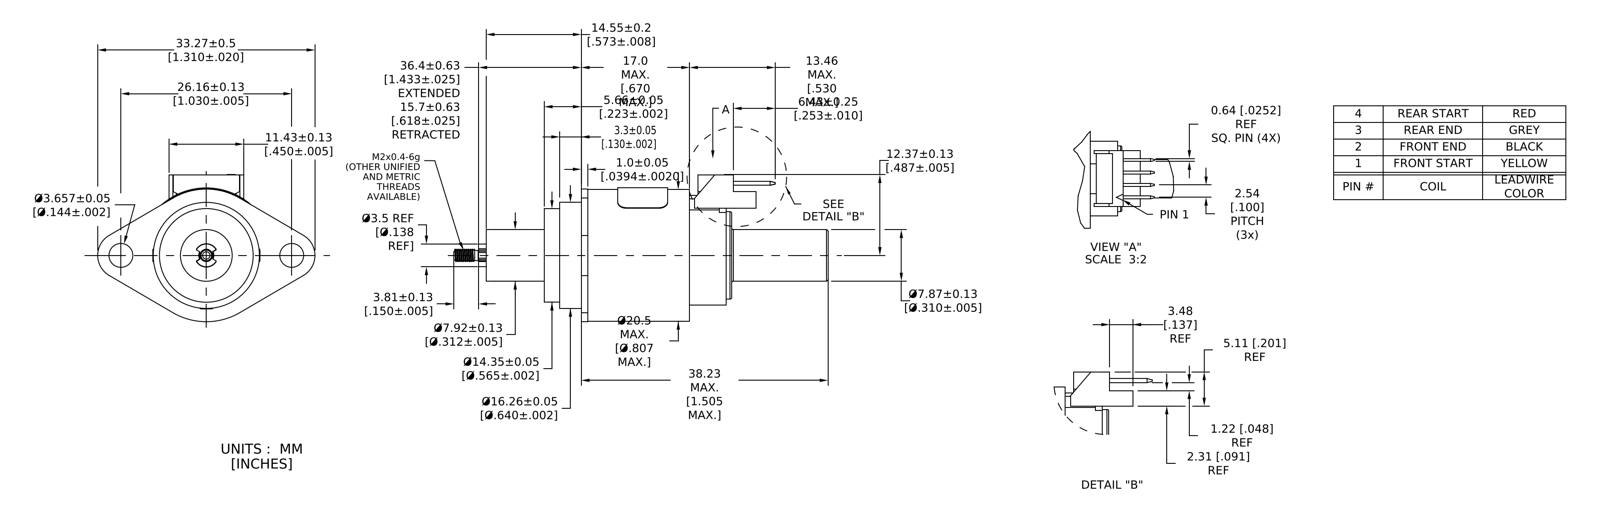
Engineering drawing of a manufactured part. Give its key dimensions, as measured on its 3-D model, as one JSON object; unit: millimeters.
{"part_name": "053NM-1526-001_4_1_1; OVERMOLD_209NM-1526-001_4_1_1; 209NM-1526-001_ASM_4_ASM_1_ASM__ASM; 149DM-1512-001_4_1_1 (+8 more)", "step_written_by": "PRO/ENGINEER BY PARAMETRIC TECHNOLOGY CORPORATION, 2014310 (CONFIG_CONTROL_DESIGN)", "units": "millimeters", "bodies": {"solids": 15, "faces": 452, "planar": 264, "cylindrical": 161, "other": 27}, "overall_size": [57.3, 33.3, 22.5], "volume_mm3": 10500, "surface_area_mm2": 8464, "round_holes": [[3.7, 2], [0.8, 1], [16, 1], [19.1, 1]], "round_bosses_or_shafts": [[20.2, 1], [19, 1], [18.4, 1], [16.3, 1], [15.2, 1], [14.4, 1], [14.2, 1], [13.4, 1]], "partial_cylinders_radius": [[0.1, 12], [0.3, 6], [0.3, 6], [0.2, 4], [3.6, 2], [1.1, 1], [1.2, 1], [1.8, 1]], "face_to_face_distances": [1, 7.7, 6.9, 0.8, 14.6, 21.2, 6.5, 22.1, 15.6, 8.7], "hole_center_spacings": [13.1, 15.9, 9.1, 26.2]}
